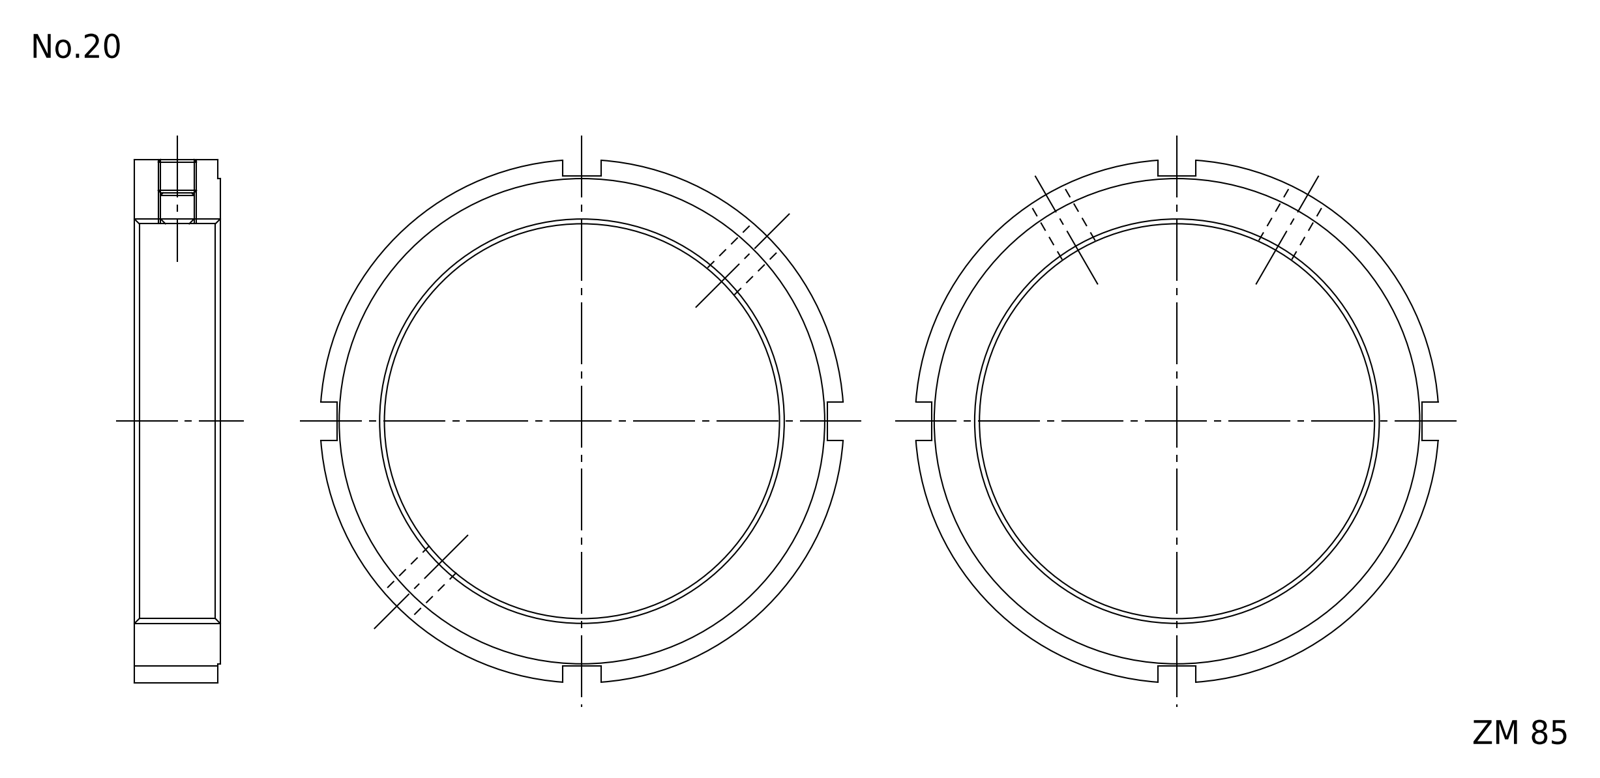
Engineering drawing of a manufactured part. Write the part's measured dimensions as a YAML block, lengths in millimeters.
part_name: "FKD ZM 85"
step_written_by: "Autodesk Inventor 2011 (AUTOMOTIVE_DESIGN)"
units: millimeters
bodies: {solids: 1, faces: 23, planar: 15, cylindrical: 8, other: 0}
overall_size: [109.71, 109.71, 18]
volume: 65452
surface_area: 19304
round_holes:
  - {diameter: 6.65, count: 2}
  - {diameter: 85, count: 1}
round_bosses_or_shafts:
  - {diameter: 110, count: 1}
  - {diameter: 102, count: 1}
face_to_face_distances: [18, 0.5, 17.5, 47.5, 55.5, 103, 8]
